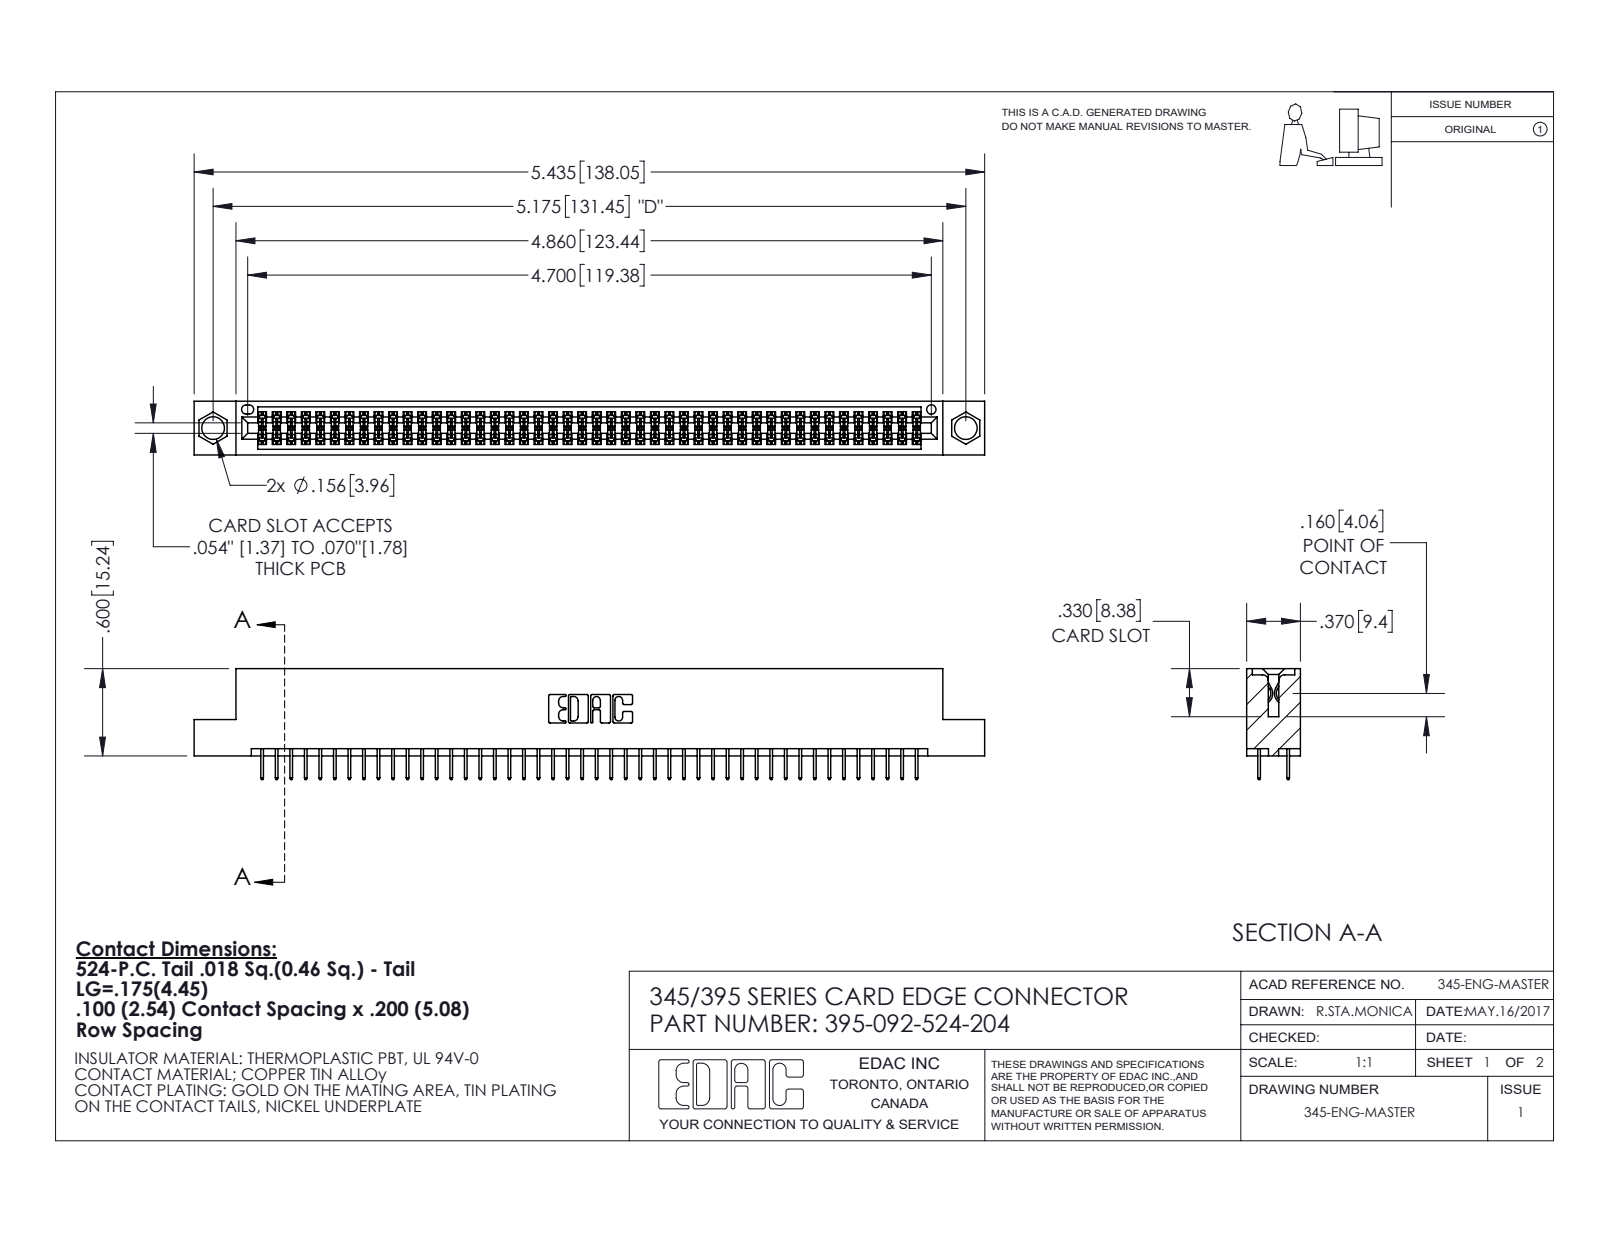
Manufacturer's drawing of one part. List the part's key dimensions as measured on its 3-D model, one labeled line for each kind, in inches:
Part name (STEP PRODUCT): 345 Part_Flush Mounting Lugs - 0.156 Dia-TI; 395-092-524-204; 345-292-001_345-293-124
STEP written by: SolidWorks 2020 (CONFIG_CONTROL_DESIGN)
Units: inches
Bodies: 93 solids, 5108 faces (3682 planar, 1426 cylindrical, 0 other)
Overall size (bounding box): 5.435 × 0.762 × 0.37
Volume: 0.806 in³ · Surface area: 29.57 in²
Round holes (diameter × count): ⌀0.156 ×2, ⌀0.064 ×1
Partial cylindrical surfaces — rounded edges, fillets, slot ends (radius × count): R0.006 ×183, R0.01 ×22, R0.007 ×6, R0.031 ×6, R0.026 ×3, R0.014 ×2, R0.019 ×2, R0.022 ×2
Main face-to-face distances: 0.072, 0.298, 0.2, 0.37, 0.098, 0.272, 0.025, 0.225, 0.072, 0.175
Hole centre spacings: 0.27, 4.939, 5.175
